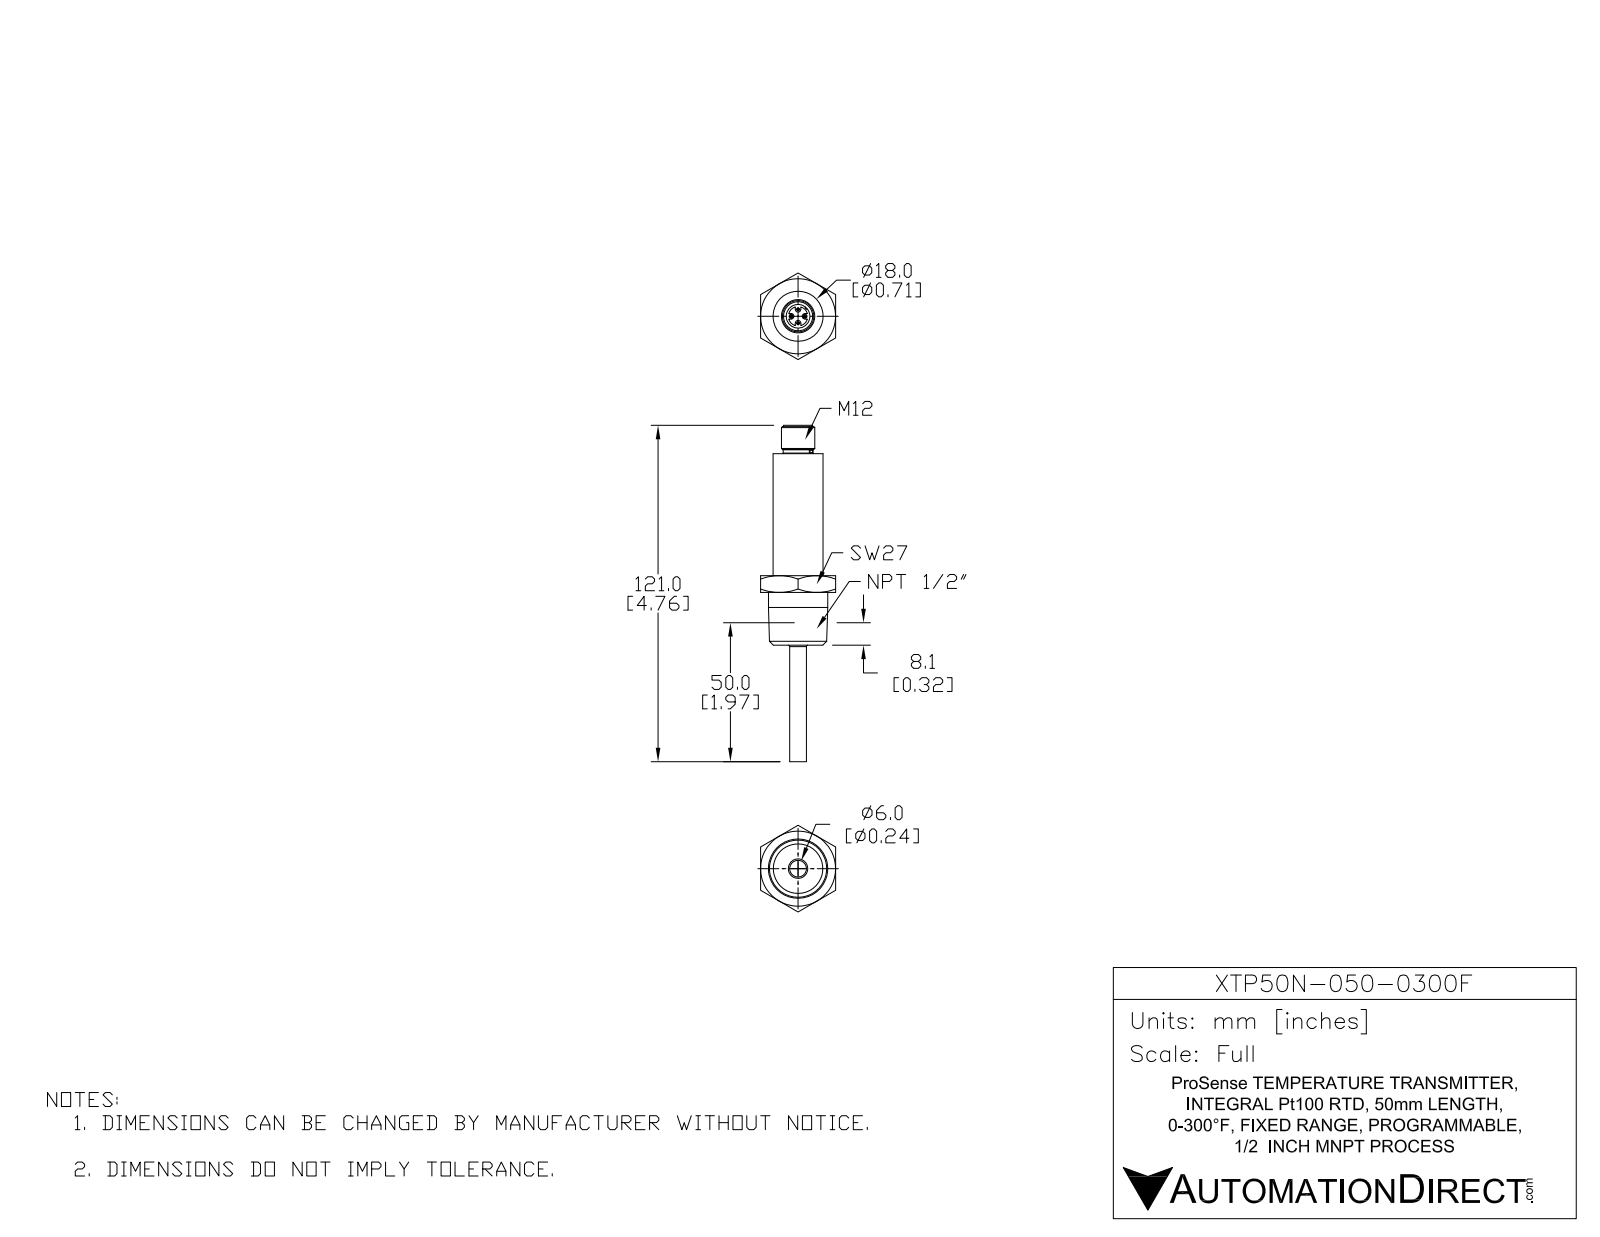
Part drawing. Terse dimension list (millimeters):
name: XTP50N-050-0300F
written by: SolidWorks 2015 (AUTOMOTIVE_DESIGN)
unit: mm
bodies: 1 solid, 117 faces (43 planar, 34 cylindrical, 40 other)
size: 121 × 31.18 × 27
volume: 22 920 mm³; area: 7 274 mm²
holes: 1× ⌀4, 1× ⌀8.5
bosses: 4× ⌀1.02, 1× ⌀21.34, 1× ⌀18, 1× ⌀12, 1× ⌀10.7, 1× ⌀10.5, 1× ⌀6
rounds: 4× R1, 1× R3.5, 1× R4.25
face distances: 27, 25, 19, 6, 68.9, 49.9, 43.9, 79.1, 60.1, 54.1
